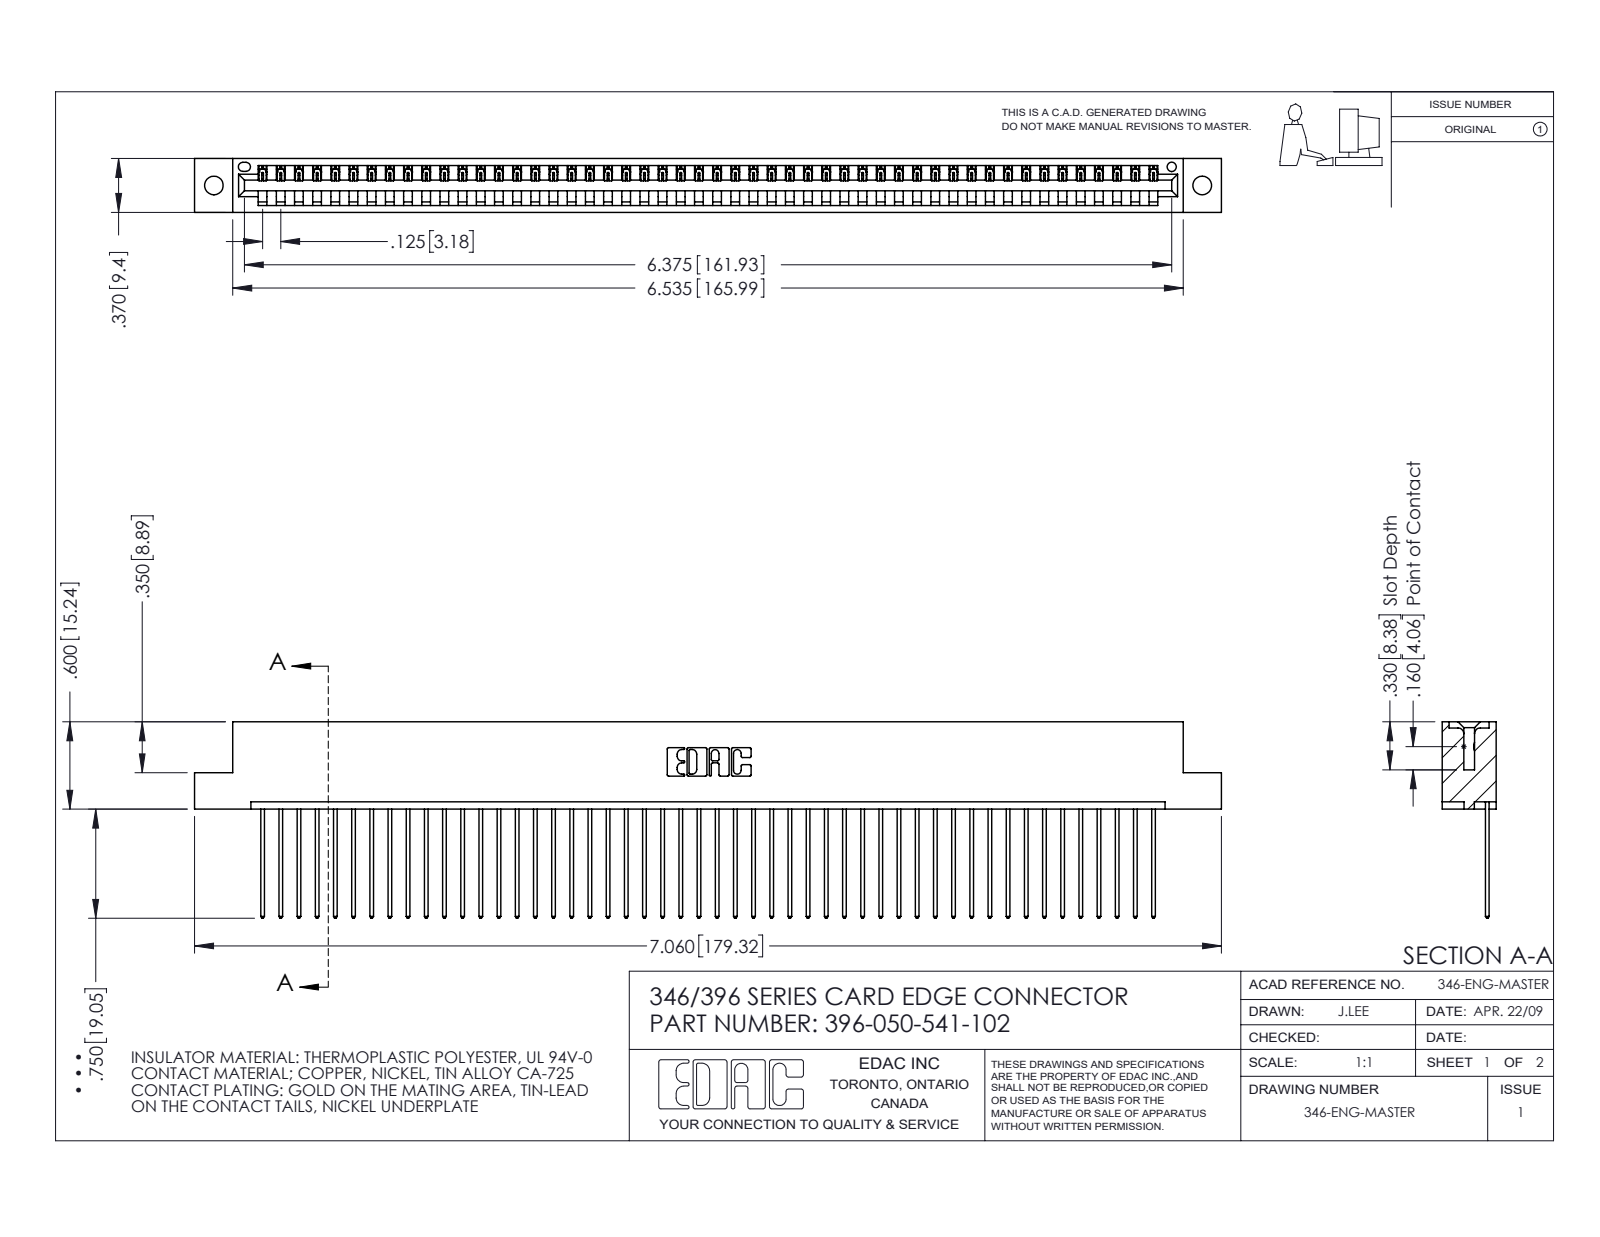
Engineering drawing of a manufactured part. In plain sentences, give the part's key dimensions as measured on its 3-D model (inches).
The part is named "396-050-541-102; 345-292-001_345-293-141; 346 Part_Flush Mounting Lugs - 0.128 Dia". Its 3-D file was written by "SolidWorks 2016 (CONFIG_CONTROL_DESIGN)". It is 51 solids with 3022 faces: 2076 planar, 946 cylindrical and 0 other. Overall it measures 7.06 by 1.35 by 0.37 inches. Its volume is 1.059 cubic inches and its surface area 34.85 square inches. Round holes: 2 of diameter 0.128, 1 of diameter 0.064. Partial cylindrical surfaces (rounded edges, fillets, slot ends): 100 of radius 0.006, 100 of radius 0.01, 22 of radius 0.01, 6 of radius 0.007, 6 of radius 0.031, 3 of radius 0.026, 2 of radius 0.031, 2 of radius 0.04. The main face-to-face distances are 0.048, 0.322, 0.37, 0.25, 0.072, 0.298, 0.025, 0.148, 0.222, 0.1. The hole center spacings are 0.246, 6.586, 6.795.
